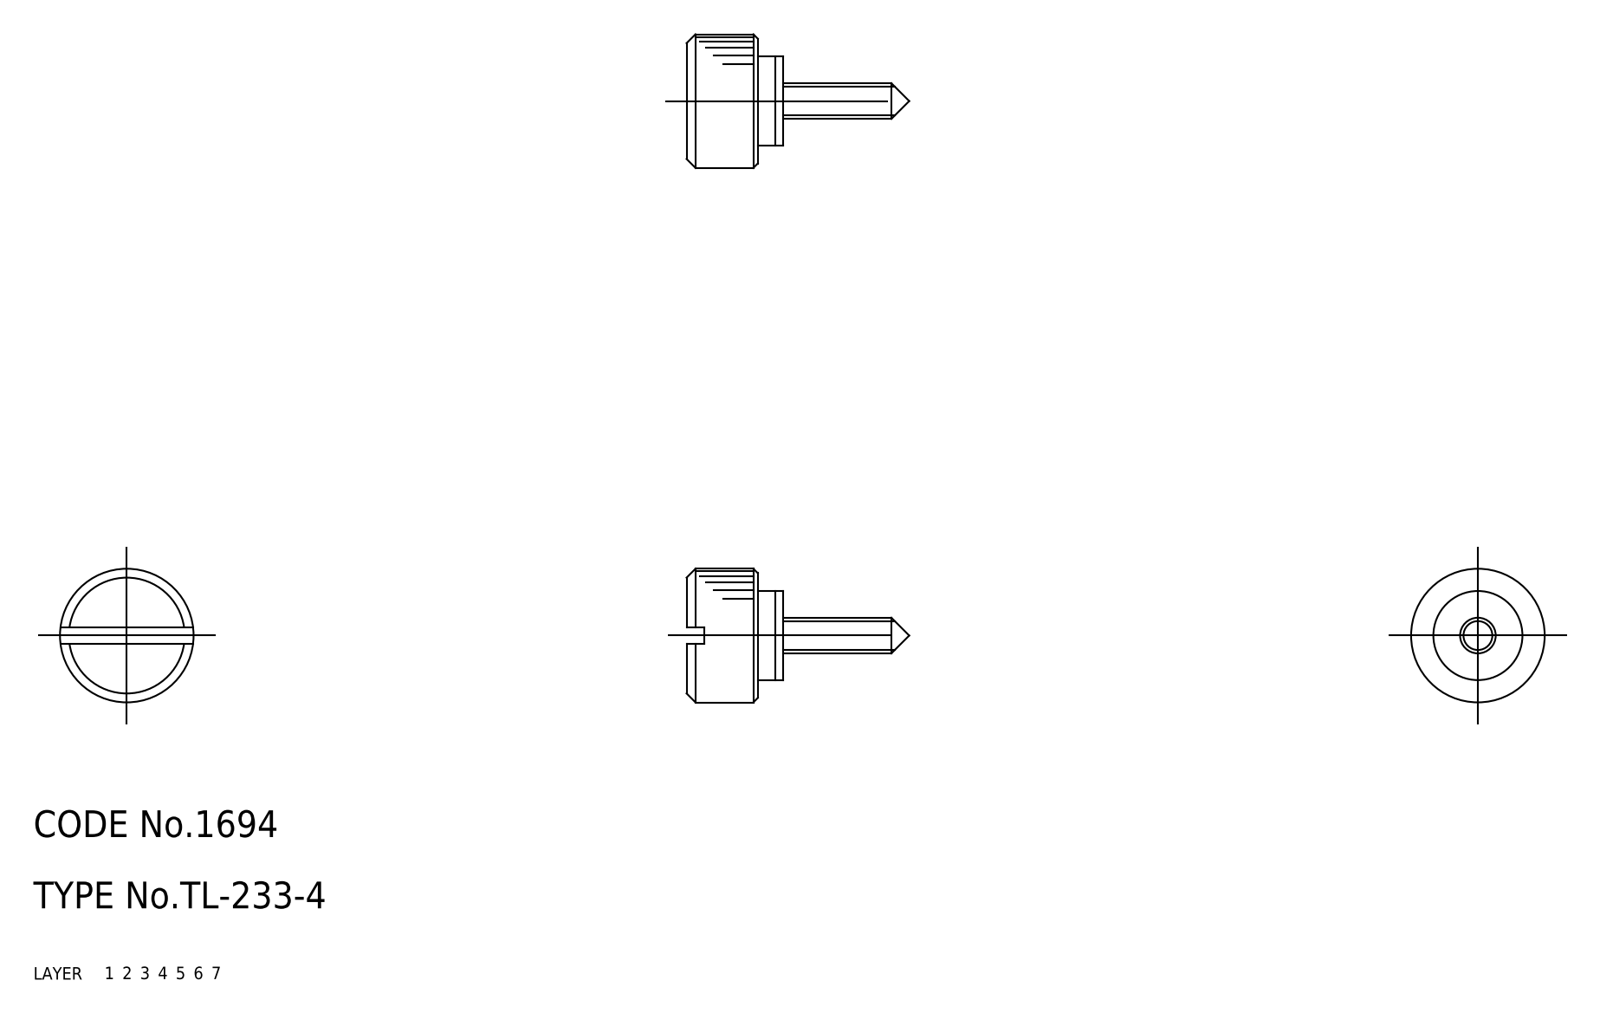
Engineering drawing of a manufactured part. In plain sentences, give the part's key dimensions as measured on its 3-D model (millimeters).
The part is named "washer; knob; TL_233_4_29120_36". Its 3-D file was written by "CADfix (AUTOMOTIVE_DESIGN)". It is 2 solids with 37 faces: 0 planar, 0 cylindrical and 37 other. Overall it measures 25 by 15 by 15 millimeters. Its volume is 1 714 cubic millimeters and its surface area 1 129 square millimeters.
